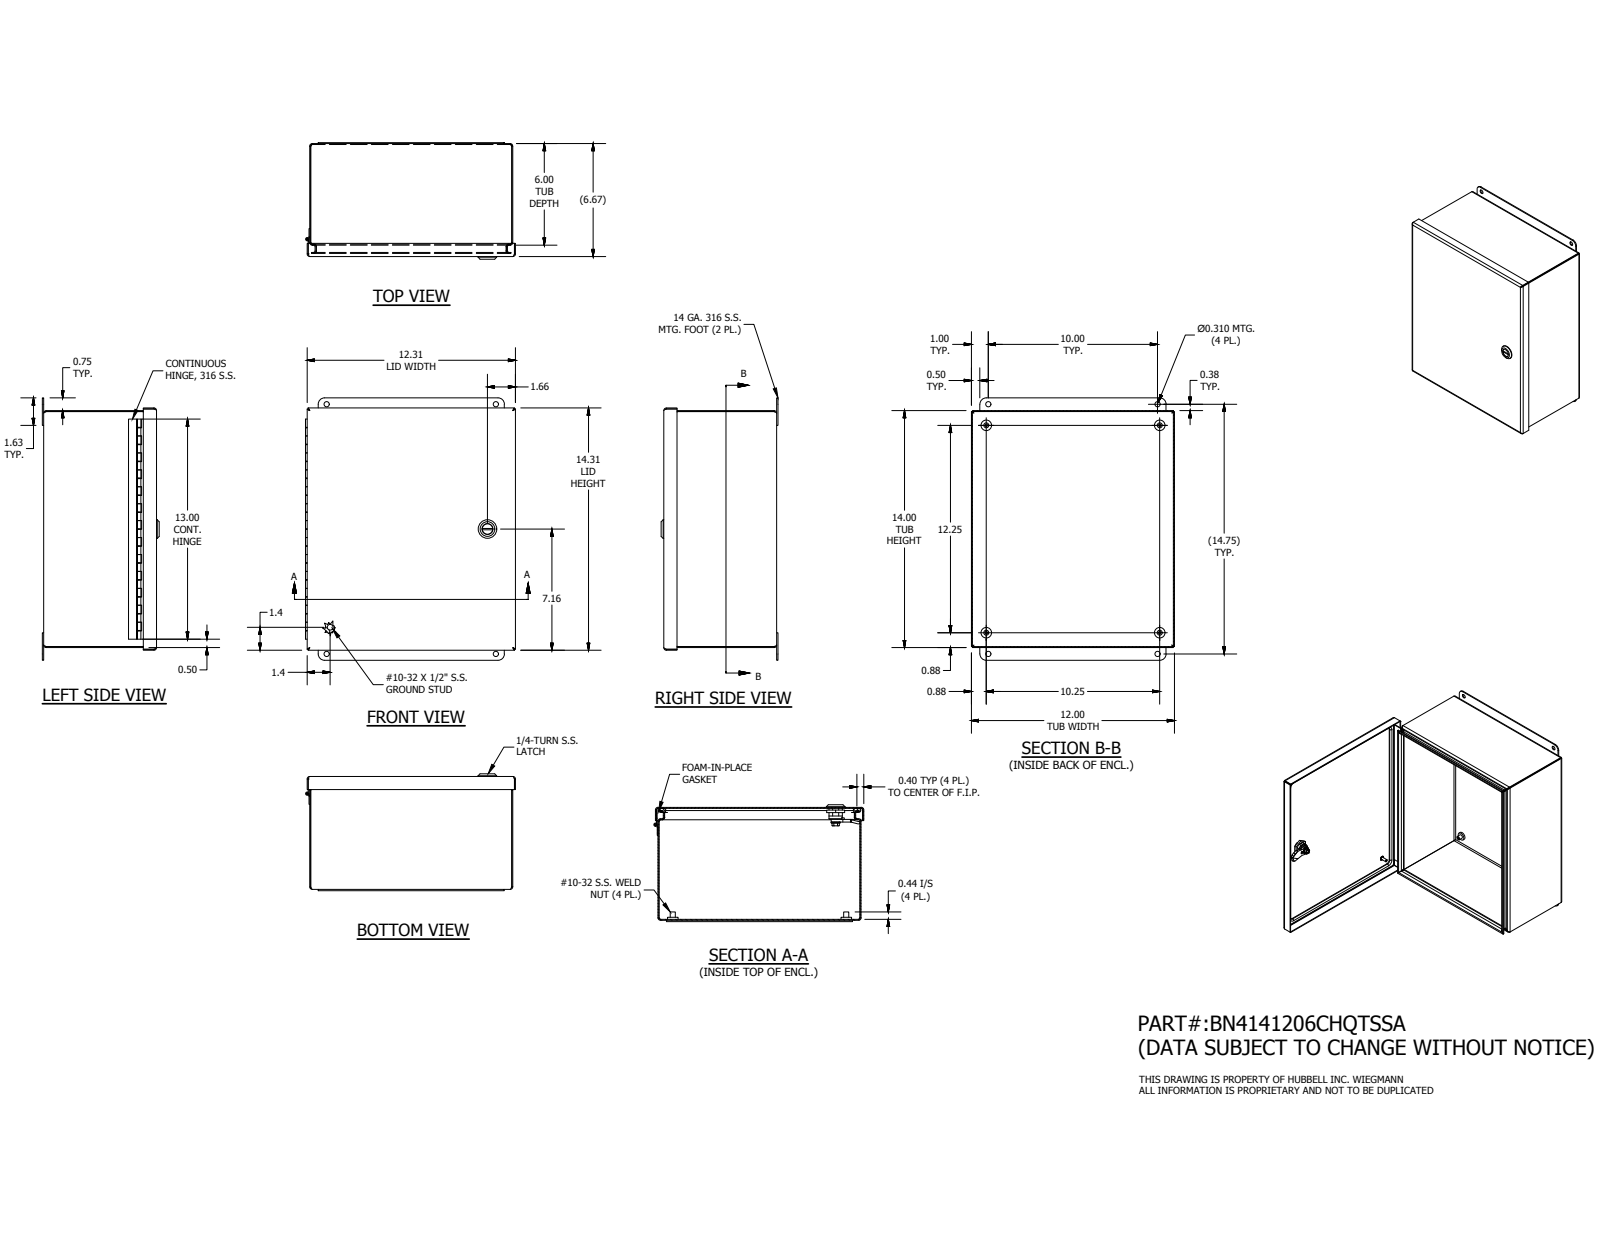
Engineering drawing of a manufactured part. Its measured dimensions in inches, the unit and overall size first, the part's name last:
Units: inches
Overall size (bounding box): 15.5 × 12.412 × 6.905
Round holes (diameter × count): ⌀0.156 ×4, ⌀0.31 ×4, ⌀0.117 ×1, ⌀0.197 ×1, ⌀0.315 ×1, ⌀0.394 ×1, ⌀0.402 ×1, ⌀0.634 ×1, ⌀0.802 ×1
Round bosses / shafts (diameter × count): ⌀0.625 ×4, ⌀0.3 ×4, ⌀1.102 ×1, ⌀0.78 ×1, ⌀0.63 ×1, ⌀0.598 ×1, ⌀0.531 ×1, ⌀0.504 ×1
Partial cylindrical surfaces — rounded edges, fillets, slot ends (radius × count): R0.094 ×20, R0.153 ×20, R0.125 ×16, R0.02 ×8, R0.157 ×4, R0.375 ×4, R0.091 ×2, R0.254 ×1
Main face-to-face distances: 0.059, 0.059, 6.614, 6.672, 6.555, 6.613, 13.941, 12, 11.941, 11.941
Hole centre spacings: 1.256, 13.5, 10, 10.202, 10.202, 10.25, 12.026, 12.25
Volume: 52.03 in³ · Surface area: 1 665 in²
Bodies: 21 solids, 691 faces (378 planar, 216 cylindrical, 97 other)
Part name (STEP PRODUCT): BN41412CHQTSSALID; 14x12; 348131; 32885LH (+8 more)
STEP written by: Autodesk Inventor 2016 (AUTOMOTIVE_DESIGN)
